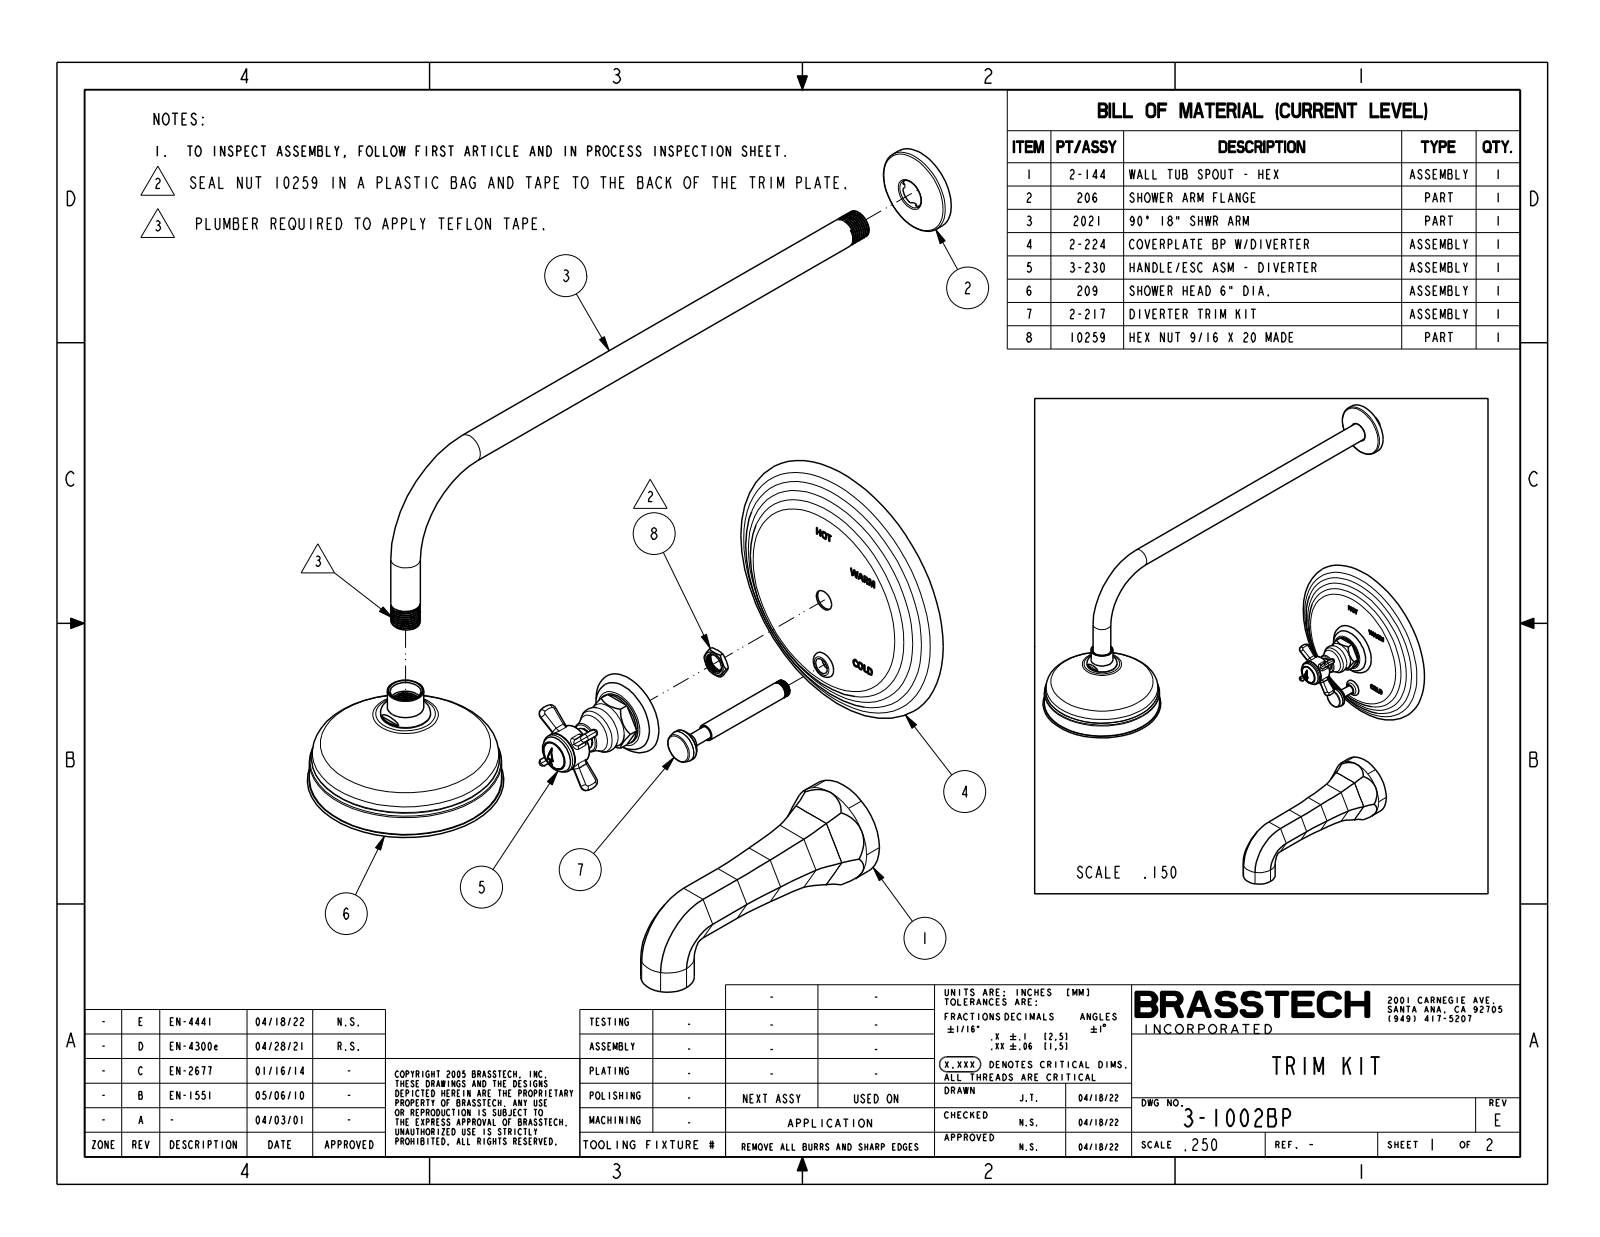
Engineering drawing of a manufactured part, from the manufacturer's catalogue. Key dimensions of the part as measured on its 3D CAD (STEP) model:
Part name (STEP PRODUCT): 3-1002BP
STEP written by: CREO PARAMETRIC BY PTC INC, 2018400 (CONFIG_CONTROL_DESIGN)
Units: inches
Bodies: 3 solids, 1087 faces (319 planar, 214 cylindrical, 554 other)
Overall size (bounding box): 22.835 × 19.701 × 7.75
Volume: 90.02 in³ · Surface area: 312.1 in²
Round holes (diameter × count): ⌀0.02 ×76, ⌀0.815 ×1, ⌀5.236 ×1
Round bosses / shafts (diameter × count): ⌀0.813 ×2, ⌀5.276 ×1, ⌀2.8 ×1, ⌀2.38 ×1, ⌀1.482 ×1, ⌀1.375 ×1, ⌀1.115 ×1, ⌀1.1 ×1
Partial cylindrical surfaces — rounded edges, fillets, slot ends (radius × count): R0.1 ×14, R2.125 ×6
Main face-to-face distances: 0.754, 0.02, 1.299, 15.037, 15.056, 0.995, 2.294, 14.041, 14.061, 12.742
Hole centre spacings: 1.417, 0.945, 1.153, 2.455, 0.472, 0.589, 1.18, 1.356
